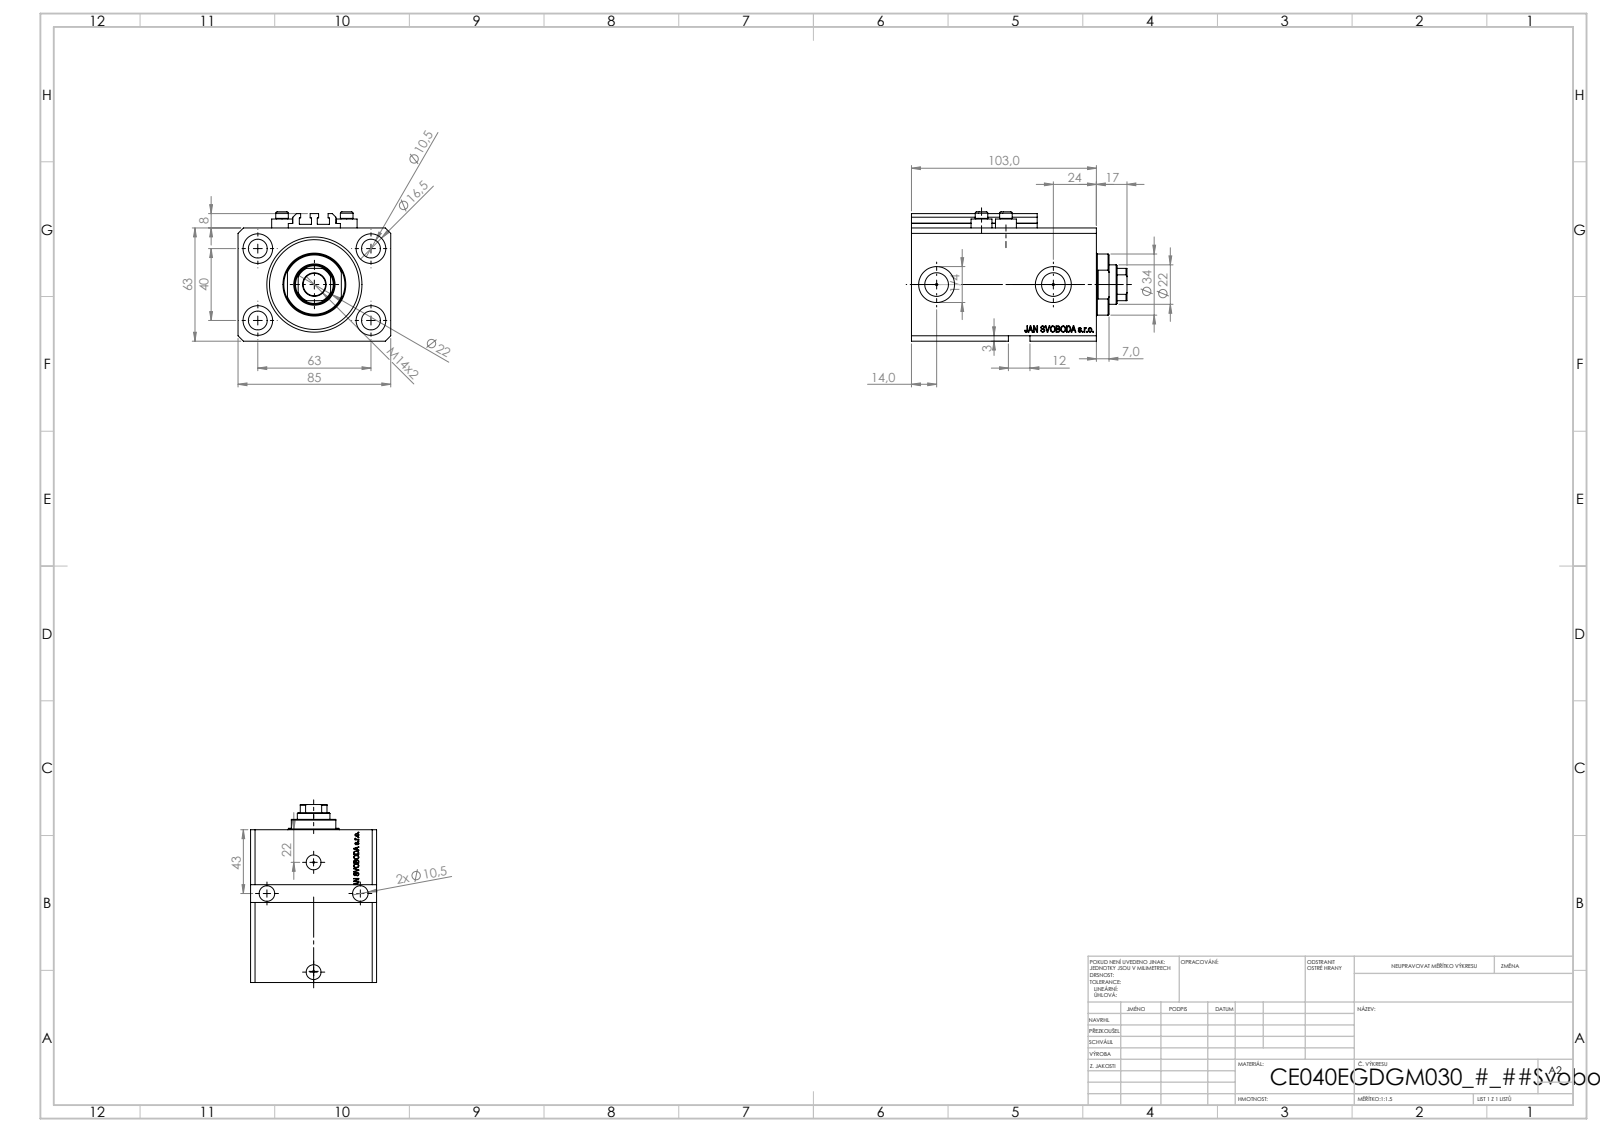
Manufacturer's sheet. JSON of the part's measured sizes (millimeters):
{"part_name": "V250CE_C_VCP; V250CE_E_Body; ALLEN BOLT V250CE; V250CE_VC_E", "step_written_by": "SolidWorks 2019 (CONFIG_CONTROL_DESIGN)", "units": "millimeters", "bodies": {"solids": 8, "faces": 1103, "planar": 539, "cylindrical": 138, "other": 426}, "overall_size": [120, 85, 72], "volume_mm3": 476033, "surface_area_mm2": 104108, "round_holes": [[10.5, 6], [1.25, 4], [4, 4], [16.5, 4], [10, 2], [13.16, 2], [20, 2], [12.5, 1], [22, 1], [40, 1], [53, 1]], "round_bosses_or_shafts": [[11.6, 4], [7, 4], [34, 1]], "partial_cylinders_radius": [[0.2, 10], [10.5, 1]], "face_to_face_distances": [63, 85, 103, 17, 86, 11.4, 74.6, 91.6, 3, 65], "hole_center_spacings": [37.31, 63, 13.6, 15.4, 24.96, 33.62, 36, 36.25]}
